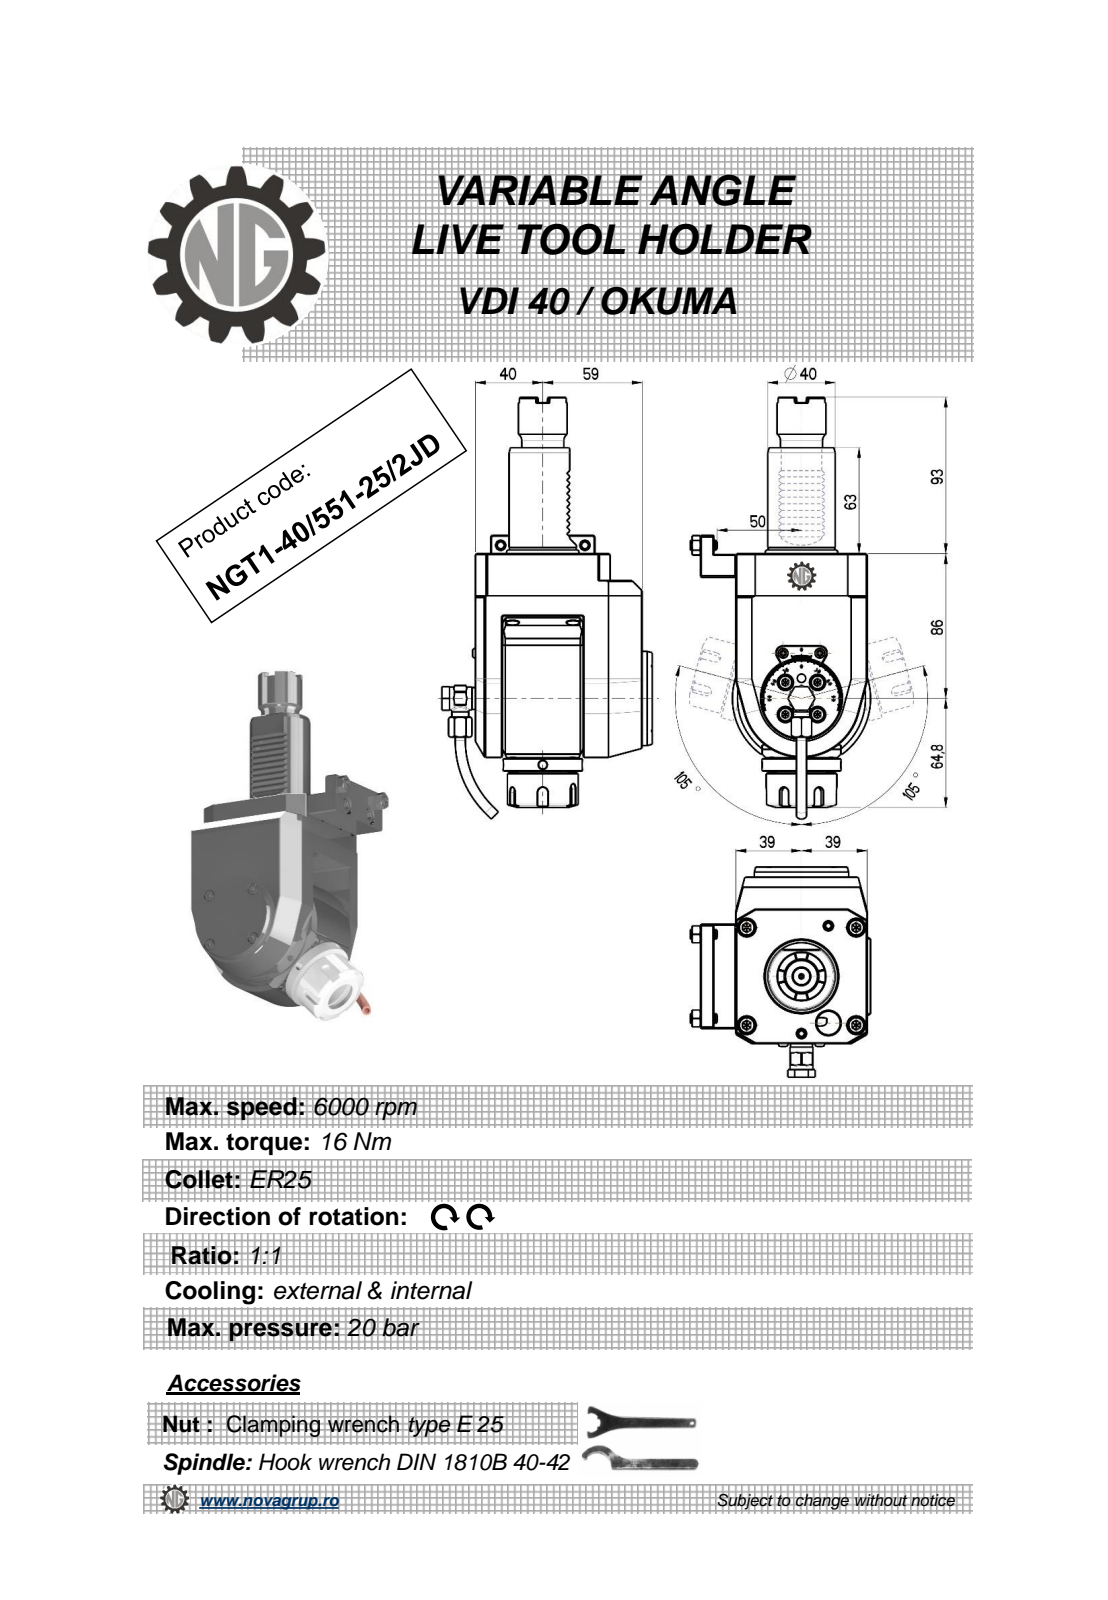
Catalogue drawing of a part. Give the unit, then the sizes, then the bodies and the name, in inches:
Units: inches
Overall size (bounding box): 9.869 × 4.917 × 4.213
Round holes (diameter × count): ⌀0.157 ×3, ⌀0.197 ×2, ⌀0.118 ×1, ⌀0.244 ×1, ⌀0.354 ×1, ⌀0.394 ×1, ⌀0.433 ×1, ⌀0.799 ×1
Round bosses / shafts (diameter × count): ⌀0.236 ×4, ⌀0.224 ×2, ⌀2.205 ×1, ⌀1.85 ×1, ⌀1.654 ×1, ⌀1.575 ×1, ⌀1.378 ×1, ⌀1.142 ×1
Partial cylindrical surfaces — rounded edges, fillets, slot ends (radius × count): R0.012 ×10, R0.012 ×10, R0.118 ×5, R0.02 ×4, R0.394 ×3, R0.039 ×2, R0.303 ×1, R1.378 ×1
Main face-to-face distances: 3.898, 1.457, 0.63, 3.071, 0.827, 2.52, 0.236, 4.134, 1.89, 0.315
Hole centre spacings: 0.016, 1.553, 1.929, 1.945
Volume: 59.03 in³ · Surface area: 136.9 in²
Bodies: 1 solid, 609 faces (246 planar, 128 cylindrical, 235 other)
Part name (STEP PRODUCT): NGT1_40_551_25_2JD
STEP written by: PRO/ENGINEER BY PARAMETRIC TECHNOLOGY CORPORATION, 2010280 (CONFIG_CONTROL_DESIGN)
